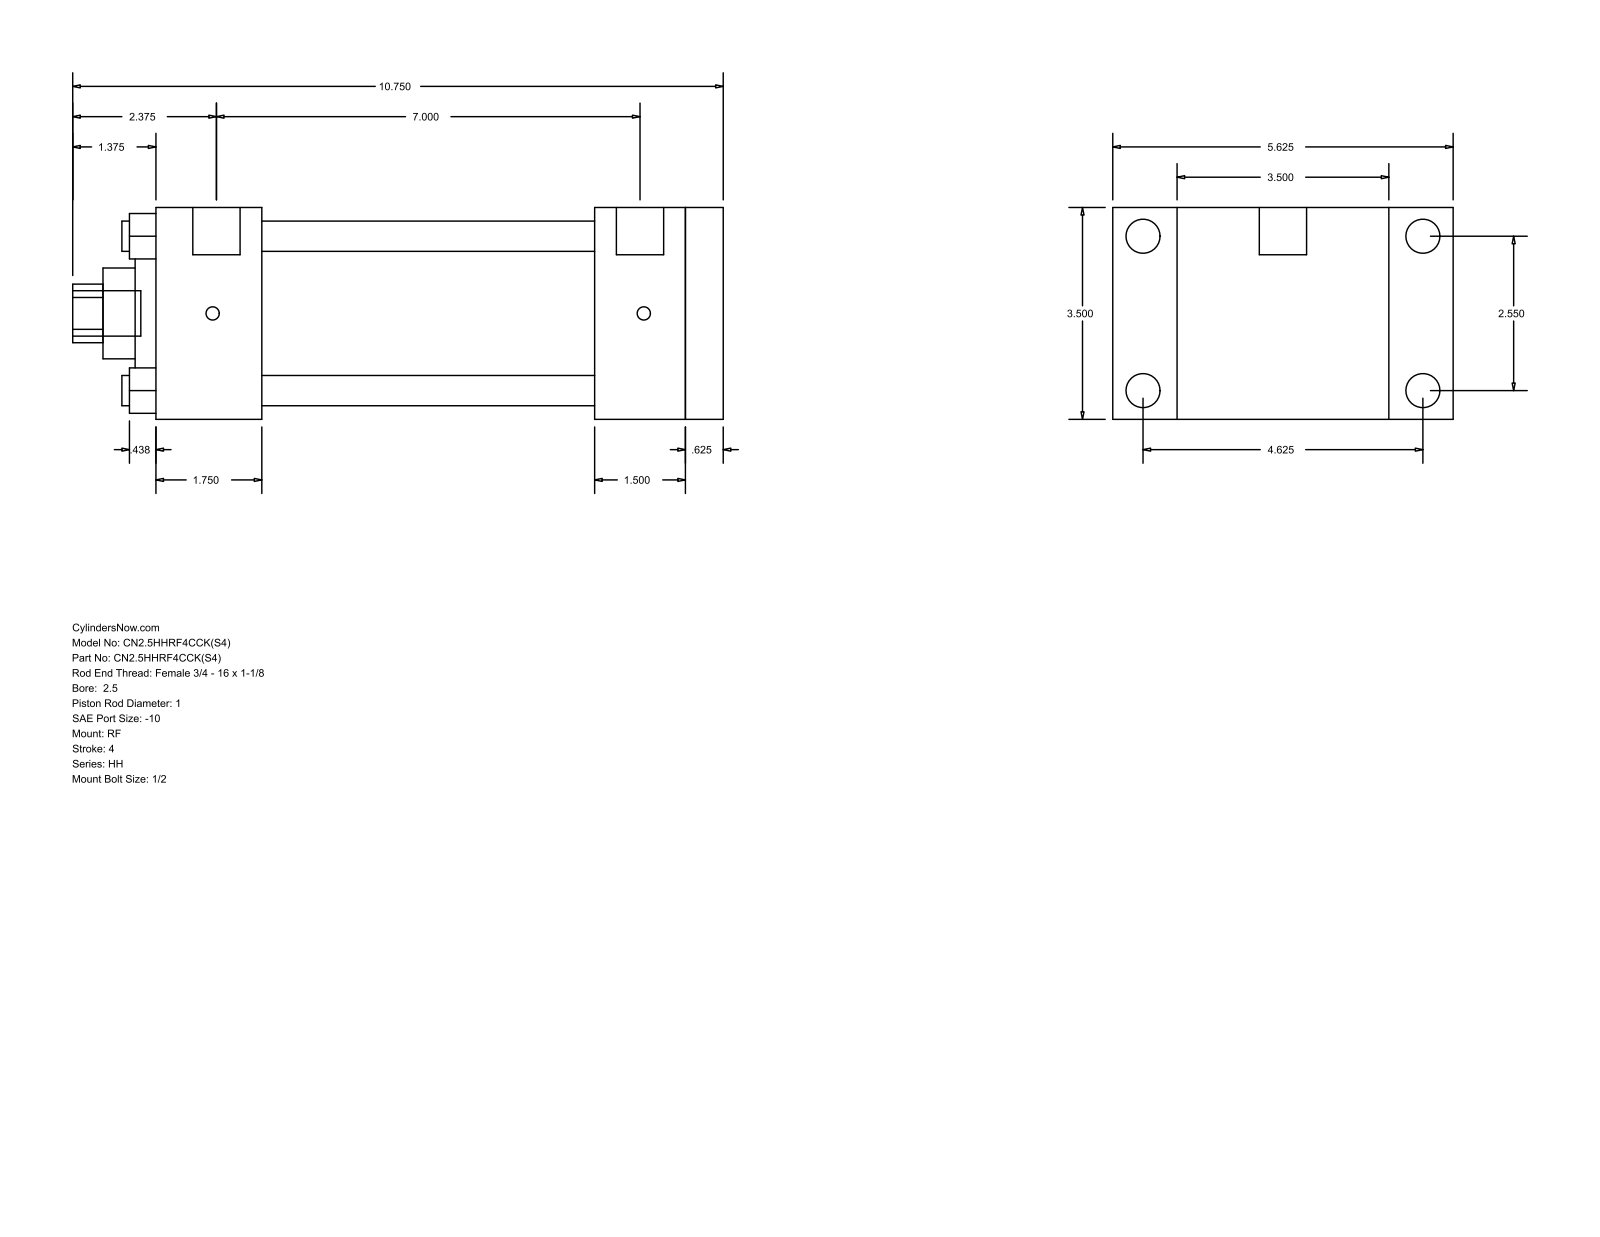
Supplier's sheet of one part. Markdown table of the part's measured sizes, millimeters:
| quantity | value |
| --- | --- |
| part name | HH_RF__0250_1 |
| STEP written by | GSSL Pune (CONFIG_CONTROL_DESIGN) |
| units | millimeters |
| bodies | 0 solids, 94 faces (65 planar, 29 cylindrical, 0 other) |
| overall size | 273.05 × 142.88 × 88.9 |
| round holes (diameter × count) | 12.7 × 4, 25.4 × 1, 38.1 × 1, 60.33 × 1, 73.03 × 1 |
| round bosses / shafts (diameter × count) | 14.3 × 4, 5.56 × 4, 19.84 × 2, 19.05 × 1 |
| partial cylindrical surfaces (radius × count) | 12.29 × 1 |
| main face-to-face distances | 88.9, 15.87, 222.26, 238.13, 44.46, 177.8, 193.67, 184.15, 139.69, 38.11 |
| hole center spacings | 45.79, 64.76, 91.58 |
